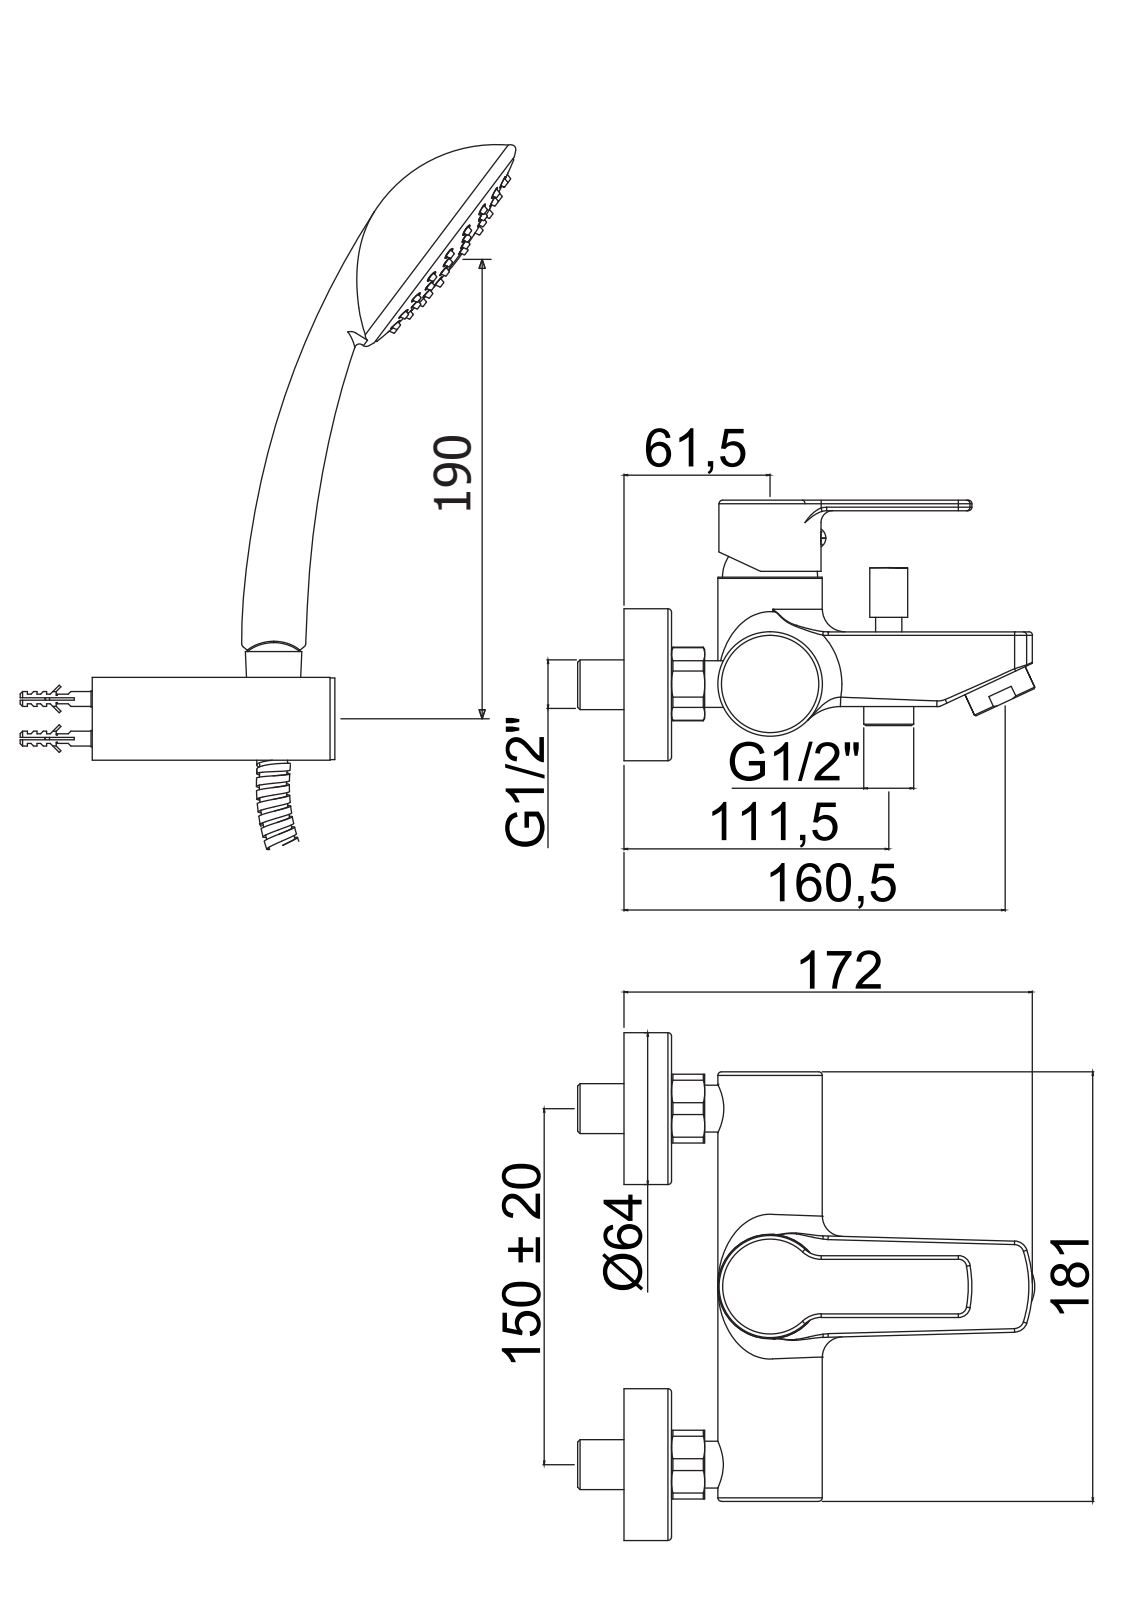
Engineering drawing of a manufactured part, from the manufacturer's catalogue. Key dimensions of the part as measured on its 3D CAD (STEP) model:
Part name (STEP PRODUCT): RED024CR
STEP written by: CREO PARAMETRIC BY PTC INC, 2020044 (CONFIG_CONTROL_DESIGN)
Units: millimetres
Bodies: 9 solids, 4879 faces (2513 planar, 874 cylindrical, 1492 other)
Overall size (bounding box): 351.6 × 335.87 × 176.33
Volume: 471 907 mm³ · Surface area: 297 161 mm²
Round holes (diameter × count): ⌀5 ×52, ⌀12 ×4, ⌀9 ×3, ⌀19 ×3, ⌀21 ×3, ⌀21.5 ×3, ⌀25 ×3, ⌀3.3 ×2, ⌀4 ×2, ⌀4.5 ×2, ⌀7 ×2, ⌀8 ×2
Round bosses / shafts (diameter × count): ⌀5 ×29, ⌀24 ×3, ⌀63.5 ×2, ⌀44 ×2, ⌀33.8 ×2, ⌀27 ×2, ⌀19.7 ×2, ⌀16 ×2
Partial cylindrical surfaces — rounded edges, fillets, slot ends (radius × count): R0.5 ×83, R1 ×32, R0.3 ×15, R0.15 ×11, R1.5 ×6, R5 ×6, R2 ×4, R5.2 ×4
Main face-to-face distances: 3.75, 0.6, 3, 27.5, 79, 6, 4, 51.5, 4.5, 56
Hole centre spacings: 39, 31, 12.2, 18.54, 24.46, 35.41, 38.67, 8
